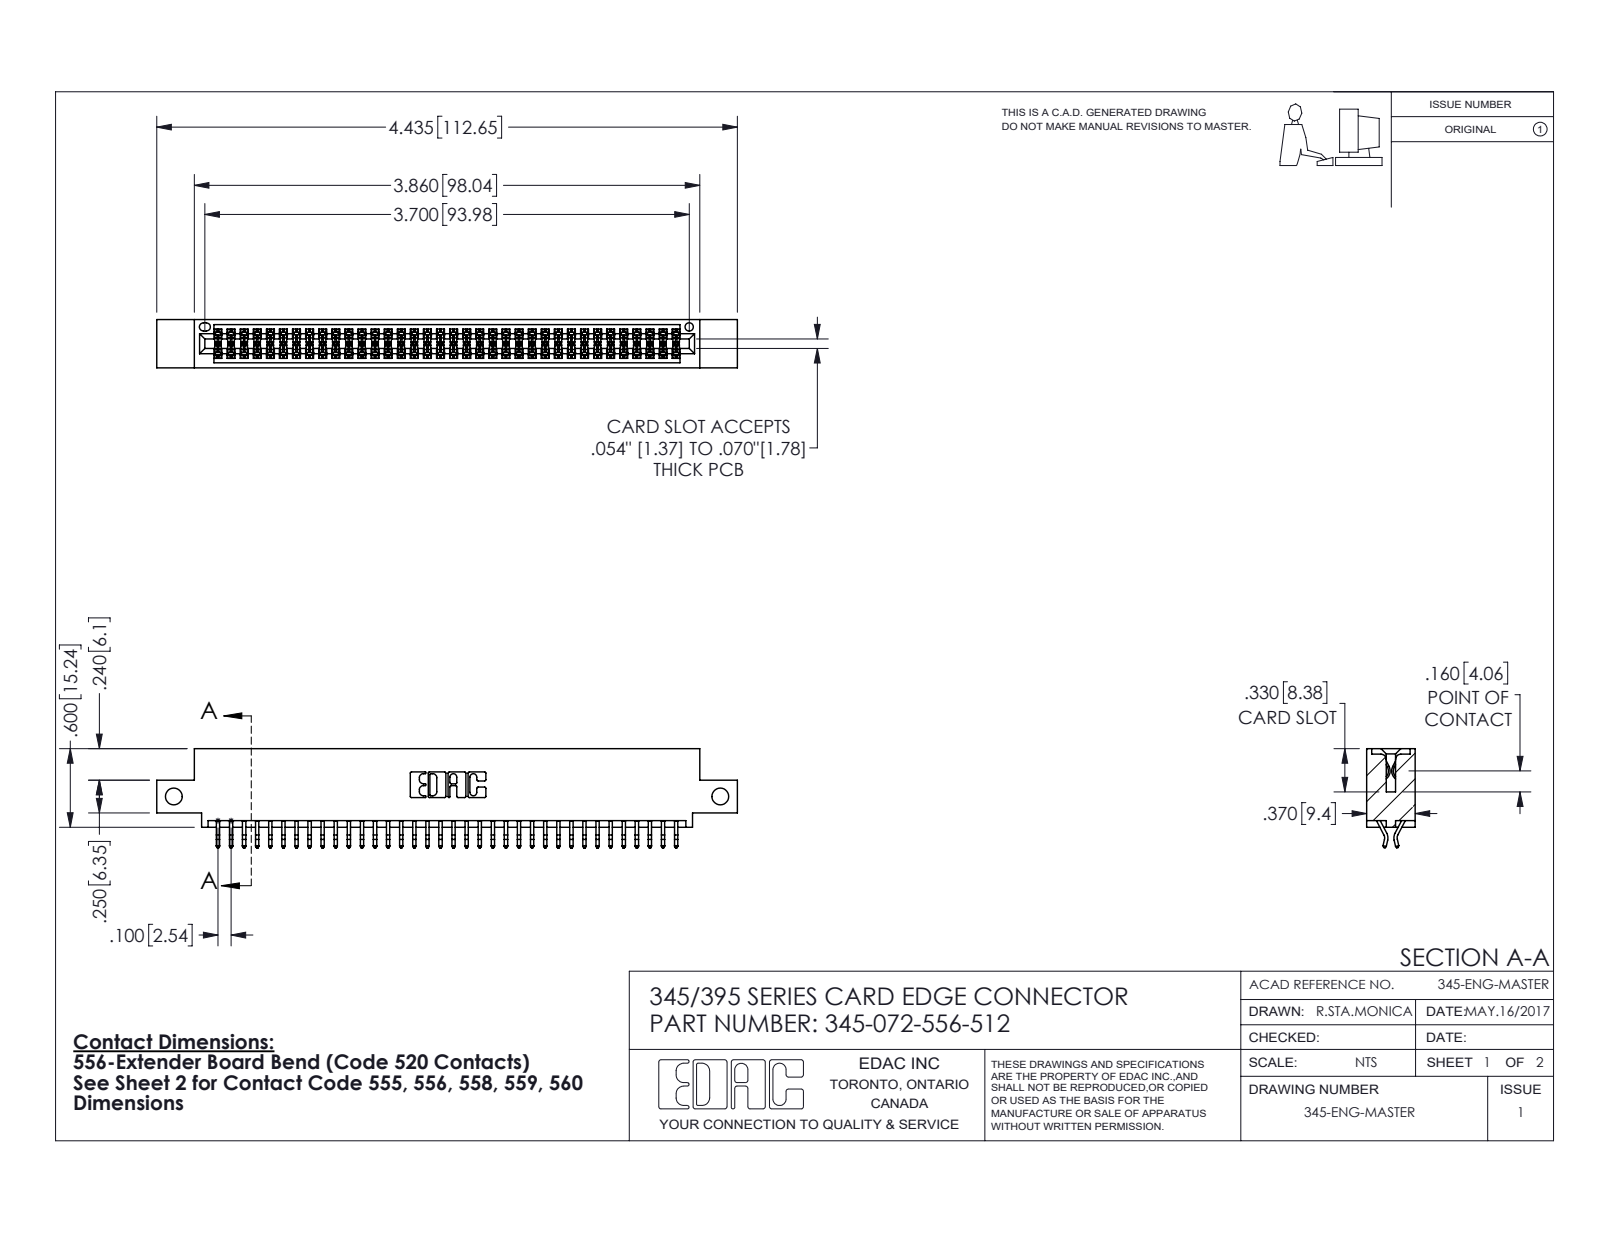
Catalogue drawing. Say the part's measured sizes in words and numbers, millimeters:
The part is named "345-292-001_556 Tail; 345 Part_0.110 Offset - Side Mount; 345-072-556-512". Its 3-D file was written by "SolidWorks 2016 (CONFIG_CONTROL_DESIGN)". It is 73 solids with 4162 faces: 2748 planar, 1414 cylindrical and 0 other. Overall it measures 112.6 by 19.2 by 9.4 millimeters. Its volume is 10 700 cubic millimeters and its surface area 15 630 square millimeters. Round holes: 2 of diameter 3.3, 1 of diameter 1.6. Partial cylindrical surfaces (rounded edges, fillets, slot ends): 108 of radius 0.2, 22 of radius 0.3, 6 of radius 0.2, 6 of radius 0.8, 3 of radius 0.7, 2 of radius 0.3, 2 of radius 0.4, 2 of radius 0.5. The main face-to-face distances are 7.6, 1.8, 9.4, 5.1, 0.6, 2.5, 6.9, 5.7, 4.4, 3.8. The hole center spacings are 106.
